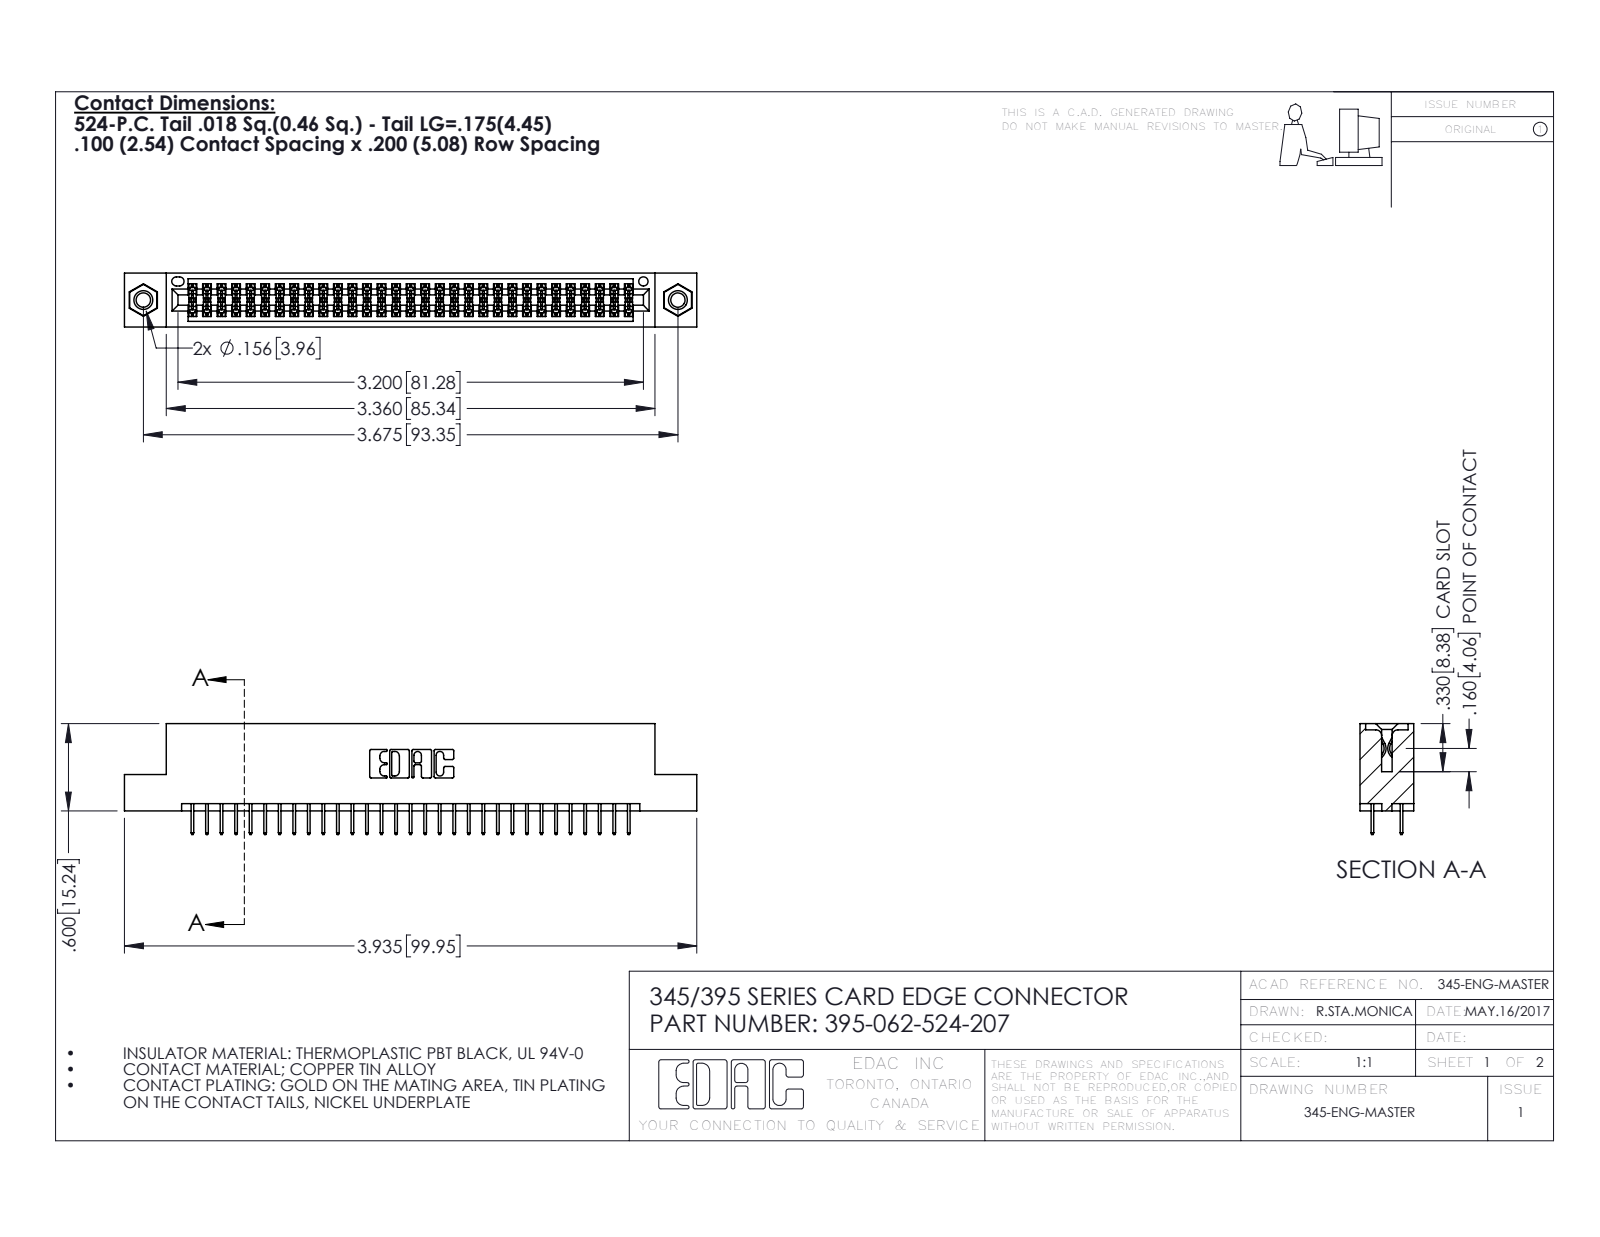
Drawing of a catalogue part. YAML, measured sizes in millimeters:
part_name: "345-250-001_345-250-005-103; 345 Part_Flush Mounting Lugs - 0.156 Dia-TI; 345-292-001_345-293-124; 395-062-524-207"
step_written_by: "SolidWorks 2016 (CONFIG_CONTROL_DESIGN)"
units: millimeters
bodies: {solids: 65, faces: 3534, planar: 2530, cylindrical: 988, other: 16}
overall_size: [99.9, 19.4, 9.4]
volume: 9500
surface_area: 13610
round_holes:
  - {diameter: 2.5, count: 2}
  - {diameter: 3.2, count: 2}
  - {diameter: 4, count: 2}
  - {diameter: 1.6, count: 1}
round_bosses_or_shafts:
  - {diameter: 3.9, count: 2}
partial_cylinders:
  - {radius: 0.2, count: 93}
  - {radius: 0.3, count: 22}
  - {radius: 0.2, count: 6}
  - {radius: 0.8, count: 6}
  - {radius: 0.7, count: 3}
  - {radius: 0.4, count: 2}
  - {radius: 0.5, count: 2}
  - {radius: 0.6, count: 2}
face_to_face_distances: [1.8, 7.6, 5.1, 9.4, 2.5, 6.9, 0.6, 5.7, 1.8, 4.4]
hole_center_spacings: [6.9, 87.4, 93.3]
